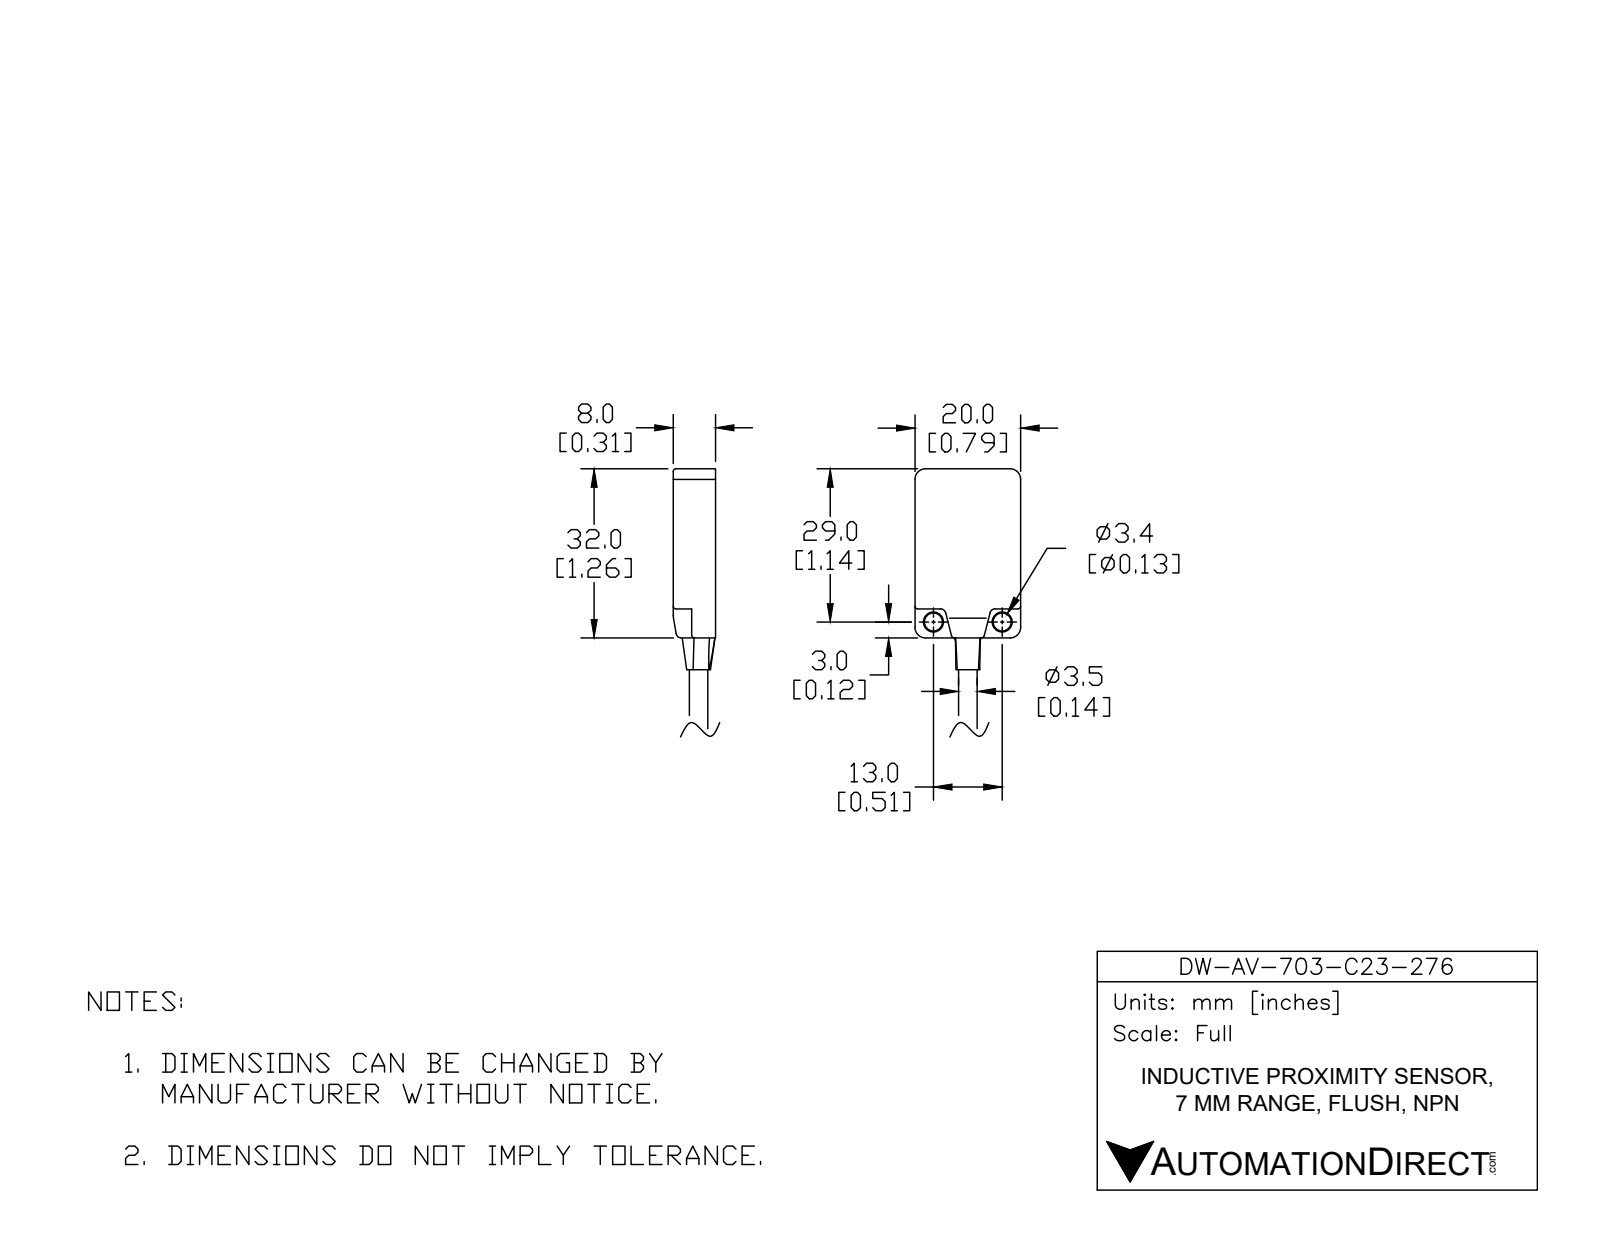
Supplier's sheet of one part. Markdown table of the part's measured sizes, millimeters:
| quantity | value |
| --- | --- |
| part name | DW-AV-702-C23-276 |
| STEP written by | SolidWorks 2017 (AUTOMOTIVE_DESIGN) |
| units | millimeters |
| bodies | 1 solid, 340 faces (203 planar, 67 cylindrical, 70 other) |
| overall size | 110 × 20 × 10 |
| volume | 6 980 mm³ |
| surface area | 3 960 mm² |
| round holes (diameter × count) | 3.4 × 2, 5.8 × 1 |
| round bosses / shafts (diameter × count) | 1 × 3, 9.8 × 1, 8 × 1, 7.5 × 1, 6.9 × 1, 6.5 × 1, 3.3 × 1 |
| partial cylindrical surfaces (radius × count) | 0.5 × 10, 2 × 8, 1 × 3, 5 × 1, 20 × 1 |
| main face-to-face distances | 8, 20, 0.9, 1.8, 4.5, 2.7, 32, 3.6, 3.5, 4.4 |
| hole center spacings | 13 |
